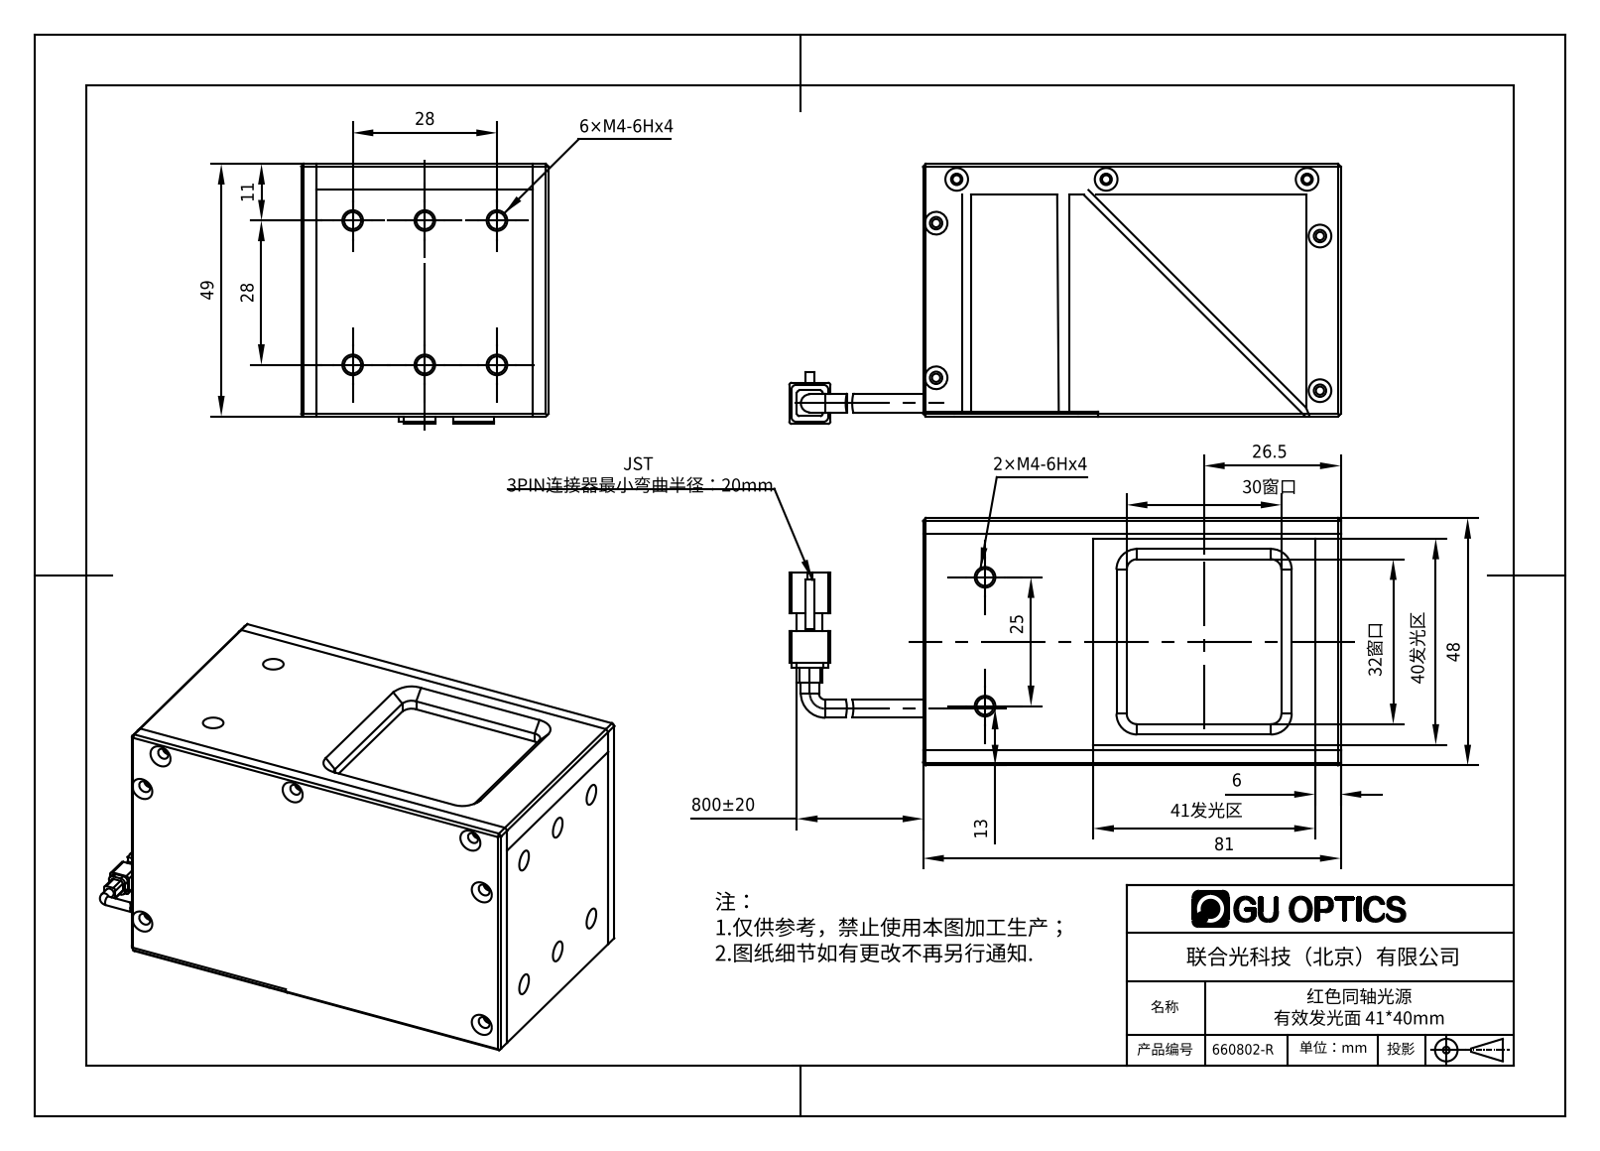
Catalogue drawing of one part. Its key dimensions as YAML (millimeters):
part_name: "红色同轴光源 有效发光面 4140mm"
step_written_by: "SolidWorks 2016 (AUTOMOTIVE_DESIGN)"
units: millimeters
bodies: {solids: 11, faces: 631, planar: 315, cylindrical: 156, other: 160}
overall_size: [95, 49, 48]
volume: 67117
surface_area: 51801
round_holes:
  - {diameter: 1.6, count: 12}
  - {diameter: 4, count: 12}
  - {diameter: 2.4, count: 8}
  - {diameter: 3.3, count: 8}
  - {diameter: 2, count: 4}
  - {diameter: 2.2, count: 3}
round_bosses_or_shafts:
  - {diameter: 1.75, count: 2}
partial_cylinders:
  - {radius: 0.5, count: 8}
  - {radius: 1, count: 4}
  - {radius: 2, count: 4}
  - {radius: 1.65, count: 1}
  - {radius: 5, count: 1}
face_to_face_distances: [1, 4, 44, 48, 3, 2, 45, 41, 42, 6]
hole_center_spacings: [28, 14, 31.3, 10.82, 15.7, 20.12, 21.78, 24]
